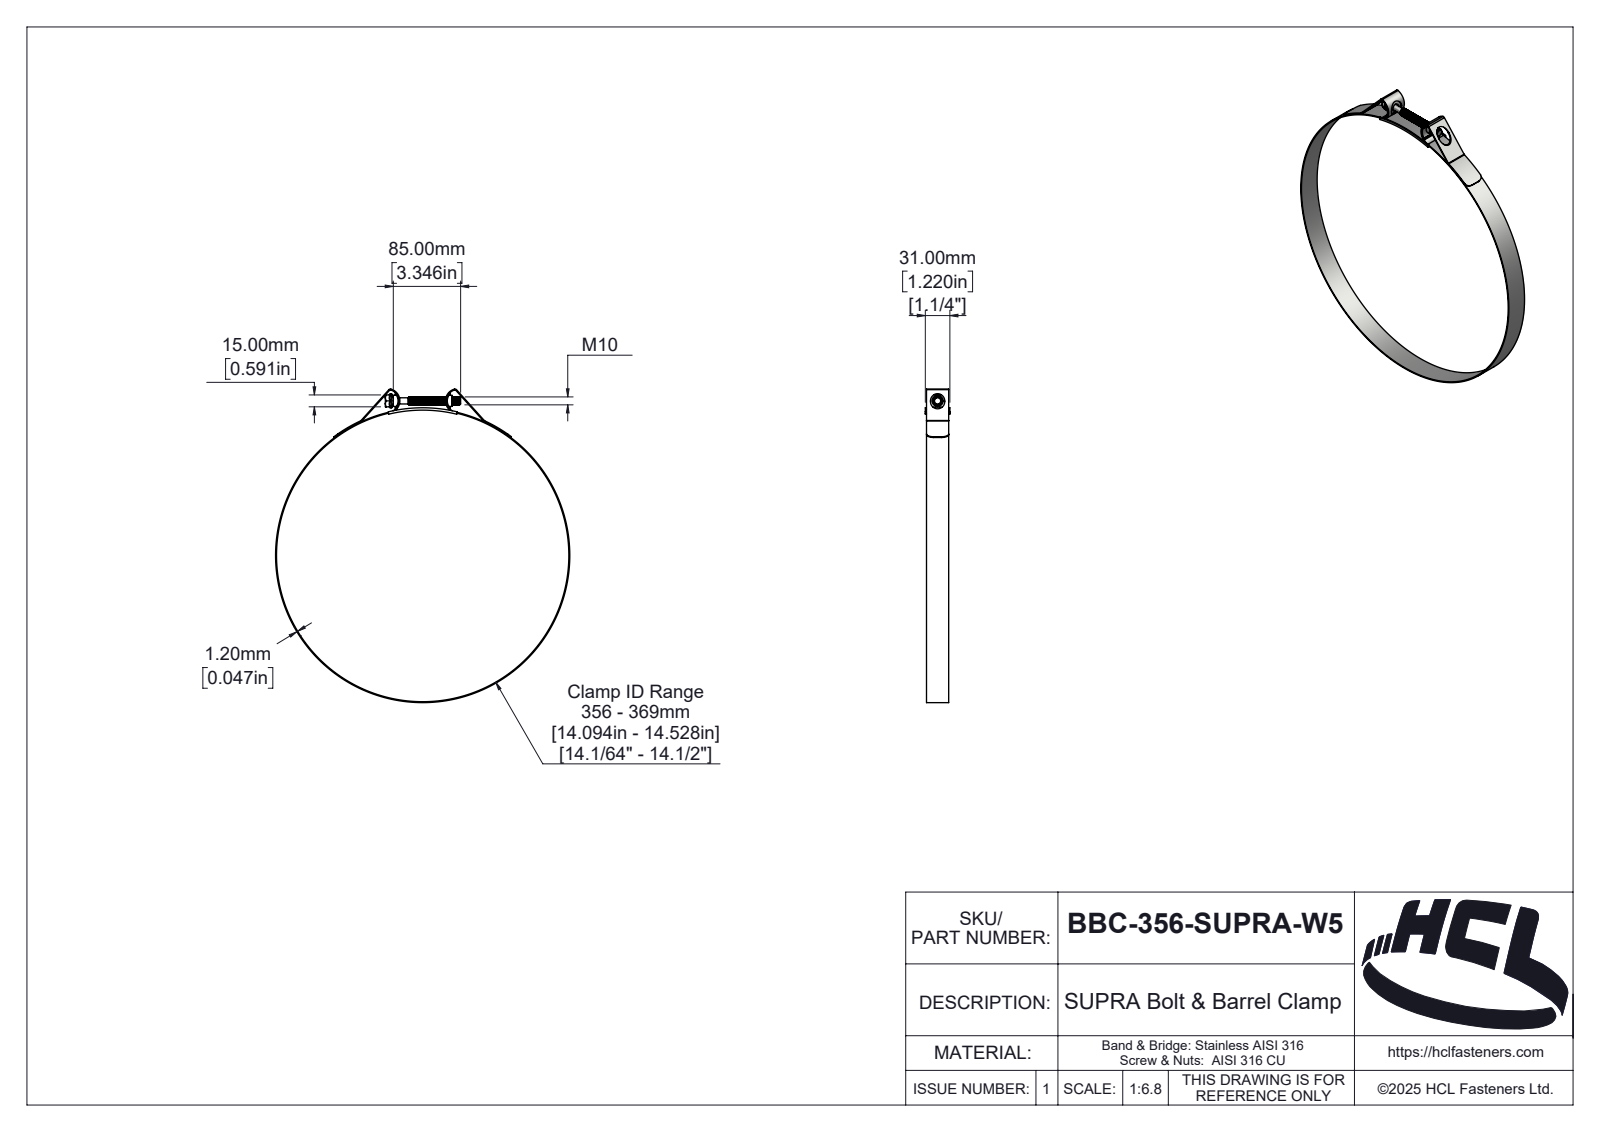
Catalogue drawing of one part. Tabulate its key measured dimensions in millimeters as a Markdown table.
| quantity | value |
| --- | --- |
| part name | BBC-356-SUPRA-W5 |
| STEP written by | SolidWorks 2025 (AUTOMOTIVE_DESIGN) |
| units | millimeters |
| bodies | 5 solids, 378 faces (50 planar, 242 cylindrical, 86 other) |
| overall size | 395.65 × 371.4 × 31 |
| volume | 56 686 mm³ |
| surface area | 90 449 mm² |
| round holes (diameter × count) | 369 × 1 |
| round bosses / shafts (diameter × count) | 371.4 × 1, 17.32 × 1, 14 × 1, 10 × 1, 7.8 × 1 |
| partial cylindrical surfaces (radius × count) | 1 × 4, 1.3 × 2, 2 × 2, 2.5 × 2, 3.2 × 2, 9 × 2, 13.13 × 2, 14.13 × 2 |
| main face-to-face distances | 1.2, 28, 1.5, 29.5, 29.8, 28.3, 31, 28.6, 15, 12.5 |
